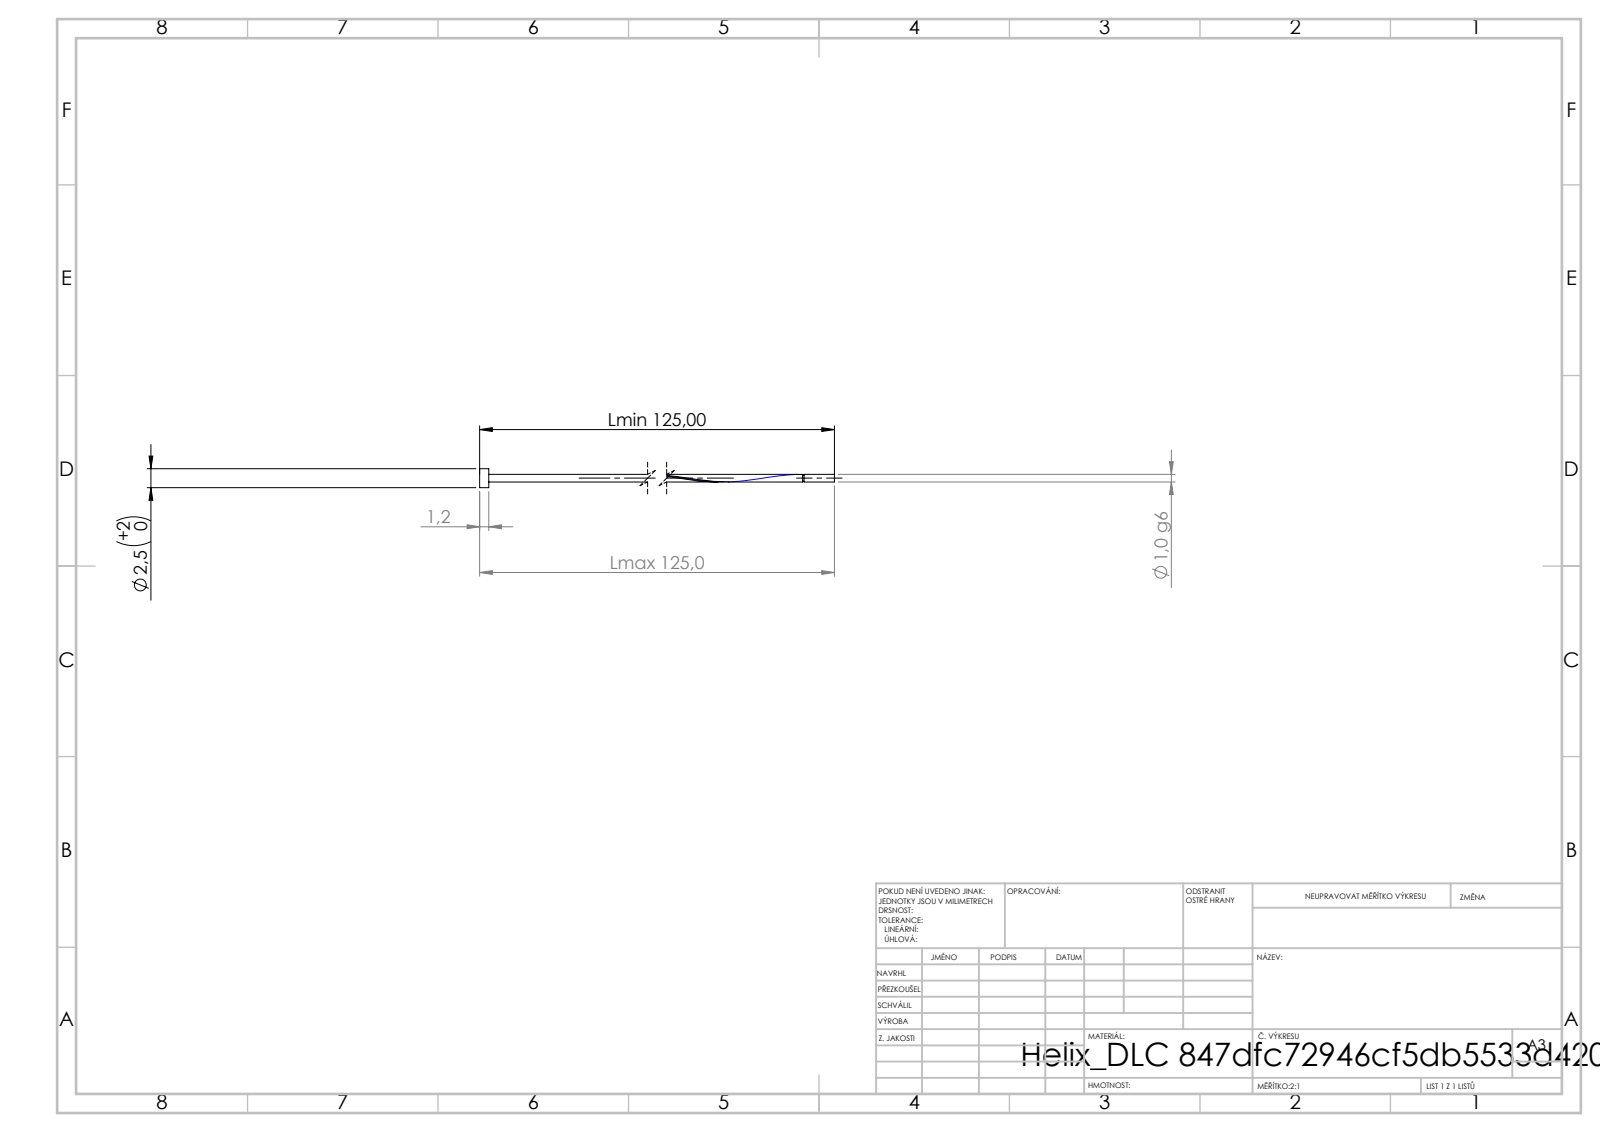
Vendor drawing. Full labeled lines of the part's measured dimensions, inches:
STEP written by: SolidWorks 2019 (CONFIG_CONTROL_DESIGN)
Units: inches
Bodies: 1 solid, 16 faces (6 planar, 9 cylindrical, 1 other)
Overall size (bounding box): 4.921 × 0.098 × 0.098
Volume: 0.008 in³ · Surface area: 0.846 in²
Round bosses / shafts (diameter × count): ⌀0.098 ×1, ⌀0.039 ×1, ⌀0.031 ×1
Main face-to-face distances: 0.047, 4.921, 4.874, 4.764, 4.717, 0.157, 4.756, 4.709, 0.165, 2.296
